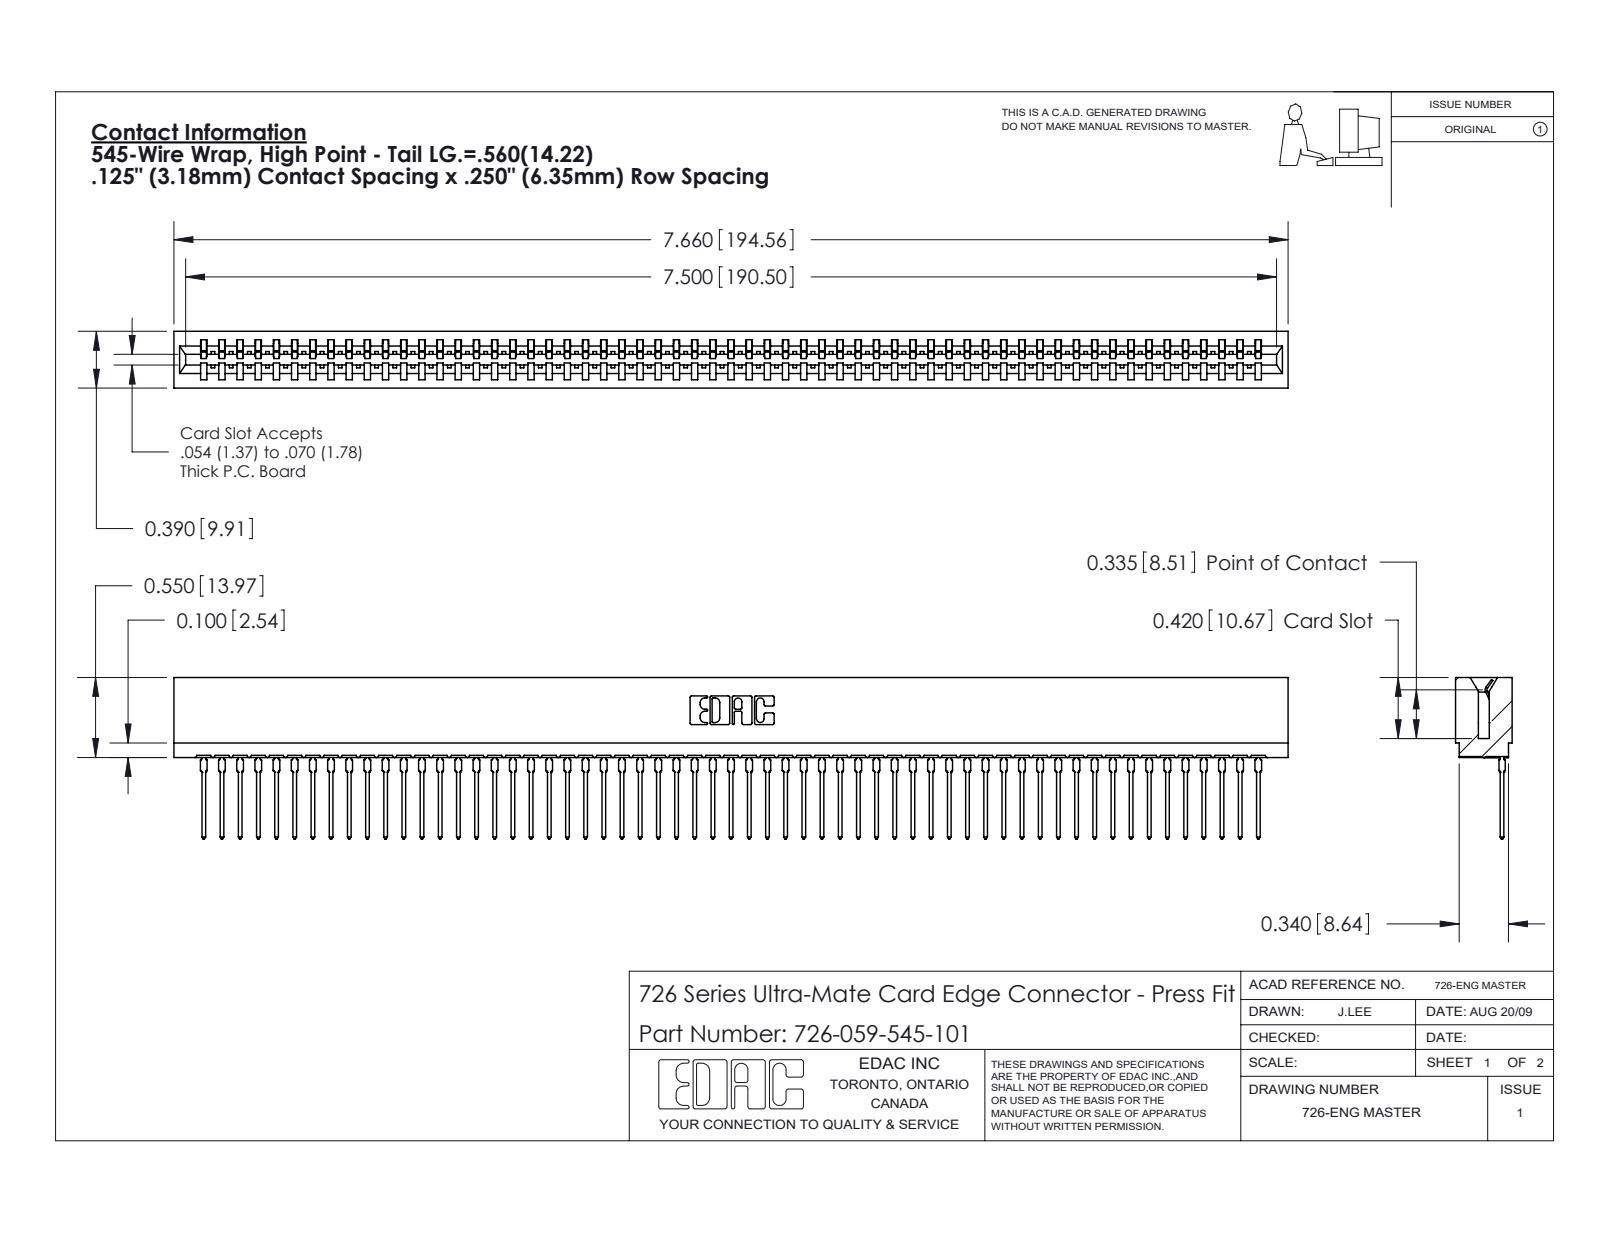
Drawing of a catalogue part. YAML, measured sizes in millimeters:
part_name: "726-059-545-101; 726 Part_.515 Slot Depth - 01; 746-292-001_545"
step_written_by: "SolidWorks 2020 (CONFIG_CONTROL_DESIGN)"
units: millimeters
bodies: {solids: 60, faces: 6469, planar: 3772, cylindrical: 1163, other: 1534}
overall_size: [194.6, 28.2, 9.9]
volume: 17440
surface_area: 27690
partial_cylinders:
  - {radius: 0.5, count: 118}
  - {radius: 0.4, count: 60}
  - {radius: 0.3, count: 22}
  - {radius: 0.2, count: 6}
  - {radius: 0.8, count: 6}
  - {radius: 0.1, count: 4}
  - {radius: 0.3, count: 4}
  - {radius: 0.7, count: 3}
face_to_face_distances: [1.4, 8.5, 9.9, 0.6, 7.8, 6.4, 2.1, 7, 9.3, 0.8]
